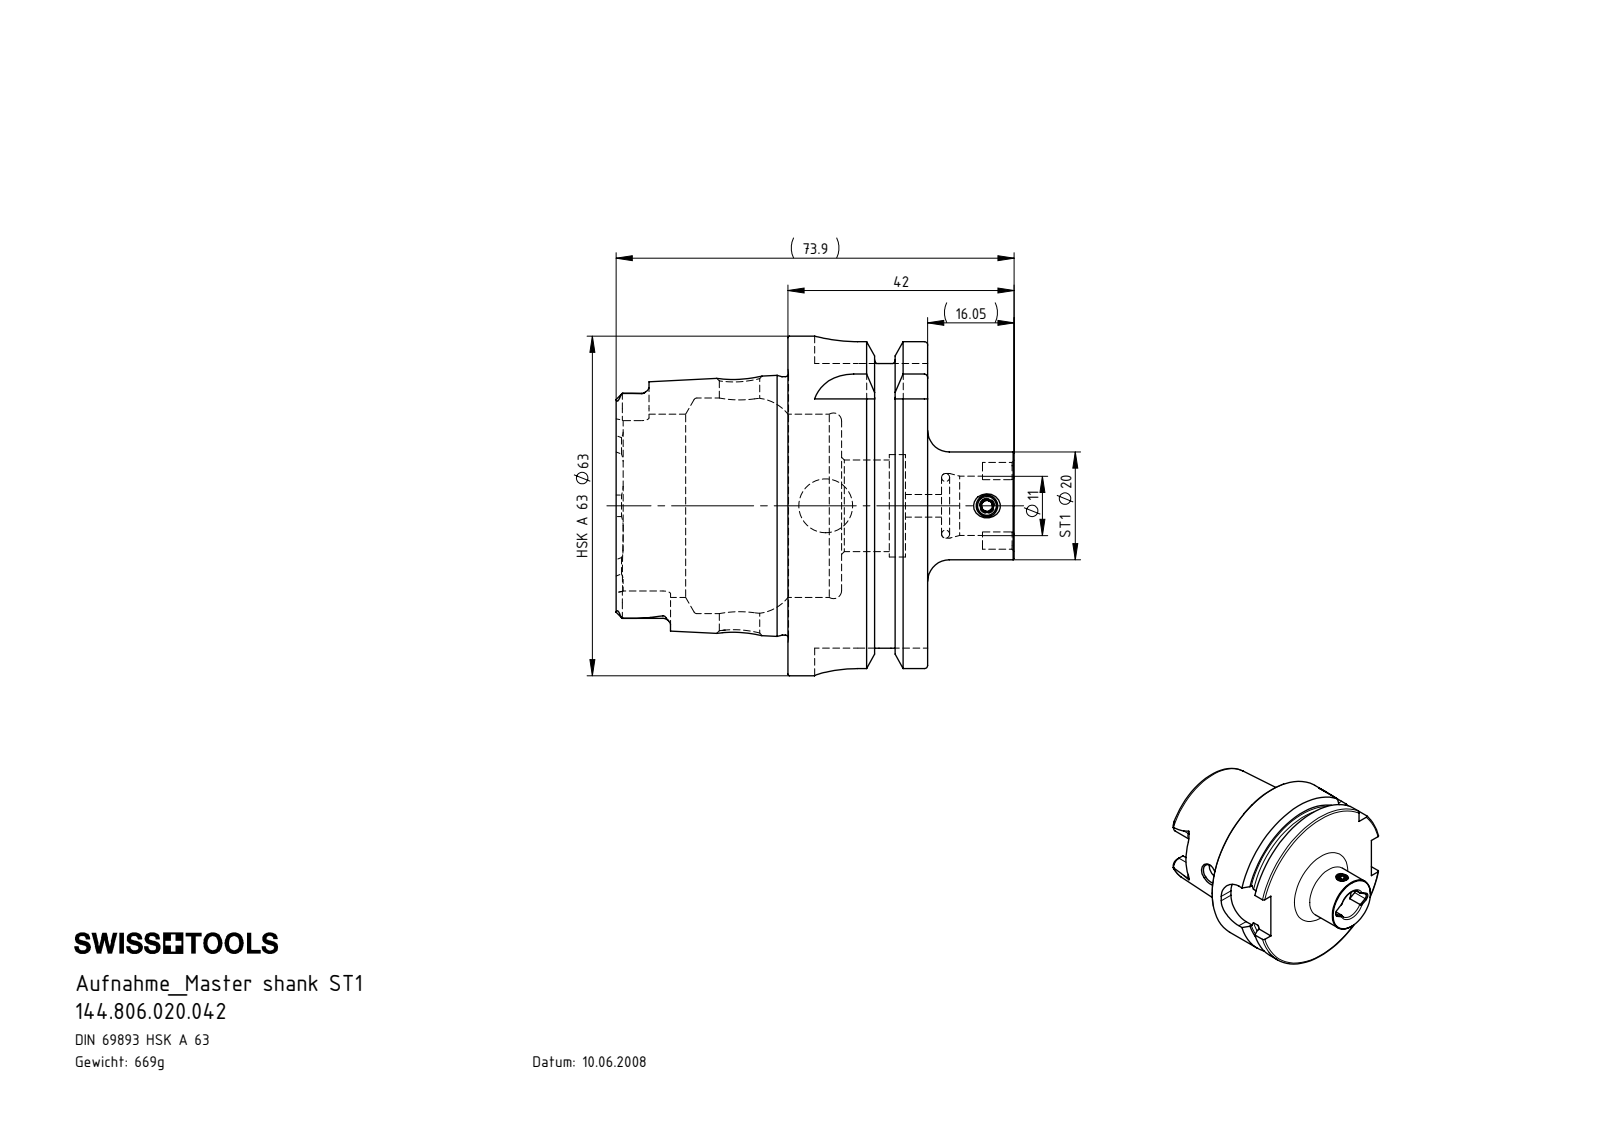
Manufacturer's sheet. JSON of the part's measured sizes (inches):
{"part_name": "DIN 3771 - 9x1.5; 144.806.020.042; HA6-ST1.K01.042_B_Fertigbearbeitung; ST1-ER1.001.005_A", "step_written_by": "SolidWorks 2017 (CONFIG_CONTROL_DESIGN)", "units": "inches", "bodies": {"solids": 3, "faces": 226, "planar": 69, "cylindrical": 57, "other": 100}, "overall_size": [2.909, 2.48, 2.48], "volume_in3": 5.204, "surface_area_in2": 37.14, "round_holes": [[0.079, 1], [0.138, 1], [0.165, 1], [0.295, 1], [0.394, 1], [0.433, 1], [0.472, 1], [0.669, 1], [0.748, 1], [1.339, 1], [1.575, 1]], "round_bosses_or_shafts": [[2.48, 1], [2.163, 1], [1.887, 1], [0.787, 1], [0.157, 1]], "partial_cylinders_radius": [[0.055, 6], [0.113, 4], [0.315, 4], [0.051, 2]], "face_to_face_distances": [1.022, 0.63, 0.392, 1.256, 1.648, 2.278, 0.858, 2.079, 0.467, 2.114], "hole_center_spacings": [1.179]}
